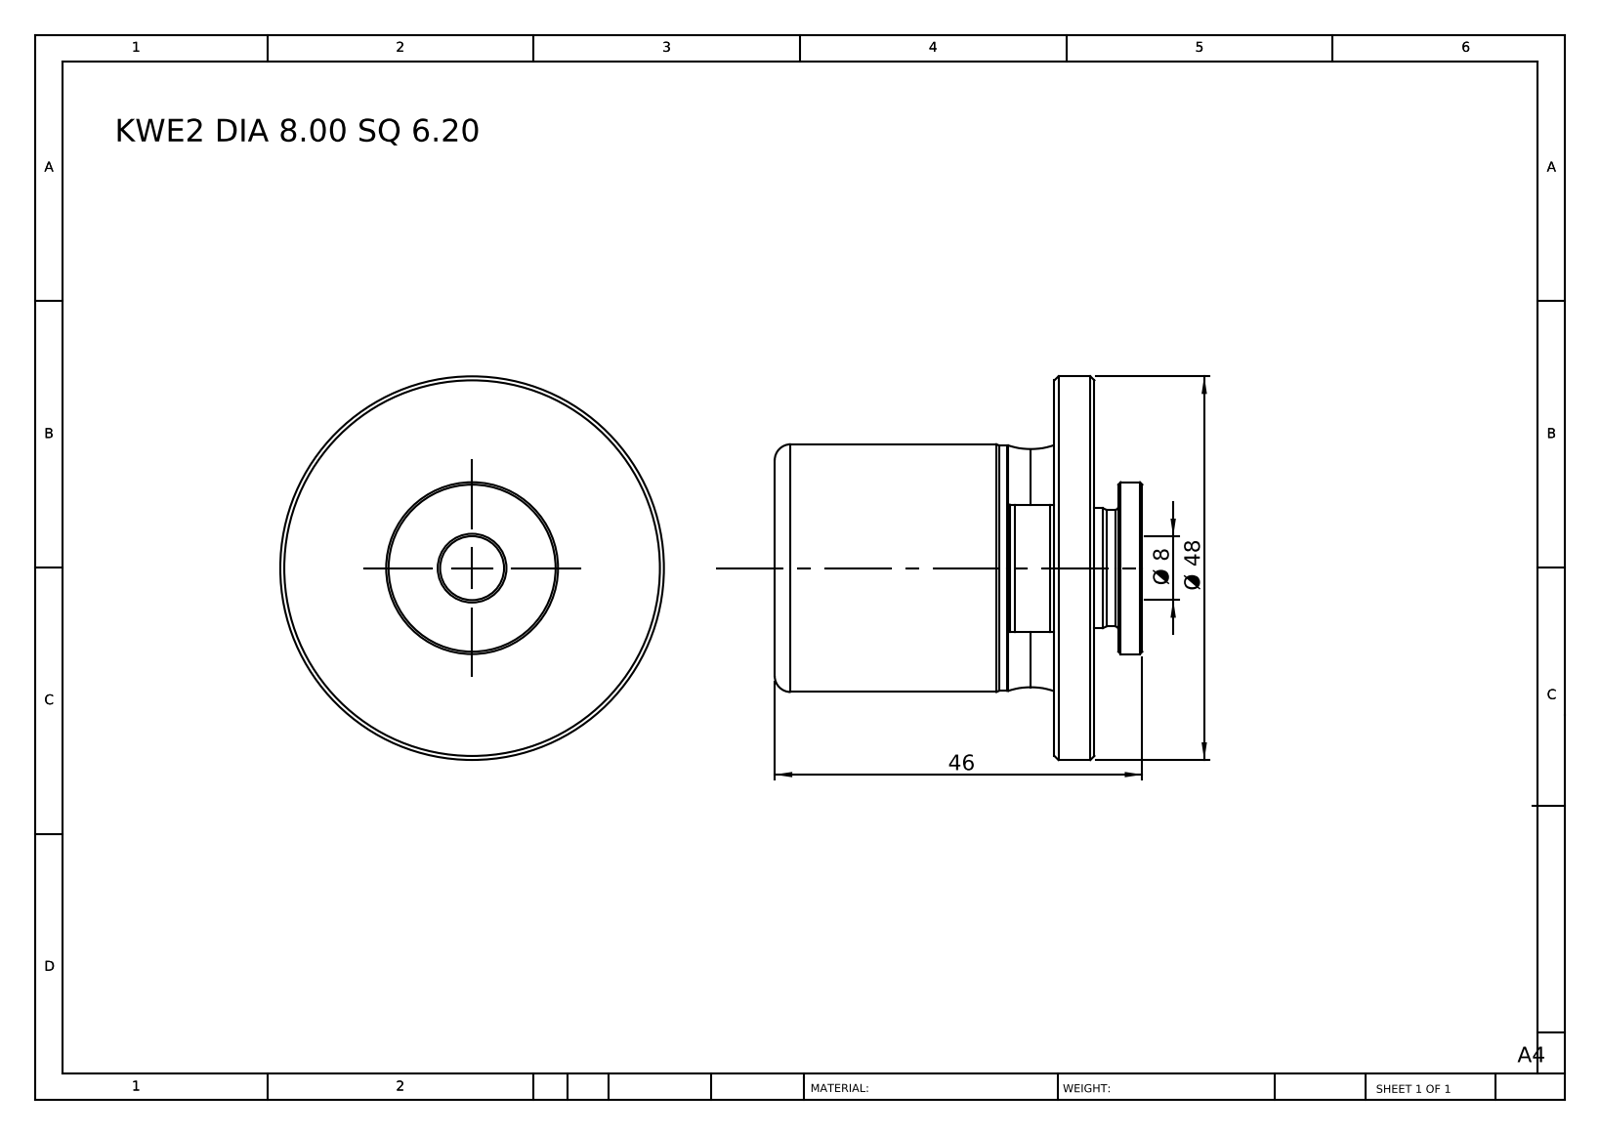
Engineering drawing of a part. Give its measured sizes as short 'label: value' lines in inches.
name: KWE2 DIA 8.00 SQ 6.20
written by: SolidWorks 2014 (CONFIG_CONTROL_DESIGN)
unit: in
bodies: 1 solid, 61 faces (12 planar, 17 cylindrical, 32 other)
size: 1.89 × 1.89 × 1.811
volume: 2.23 in³; area: 13.84 in²
holes: 1× ⌀0.315
bosses: 1× ⌀1.89, 1× ⌀1.22, 1× ⌀1.209, 1× ⌀0.846, 1× ⌀0.591, 1× ⌀0.575
rounds: 1× R0.783
face distances: 0.197, 1.378, 1.575, 0.118, 1.811, 0.433, 0.236, 1.693, 0.315, 1.161
